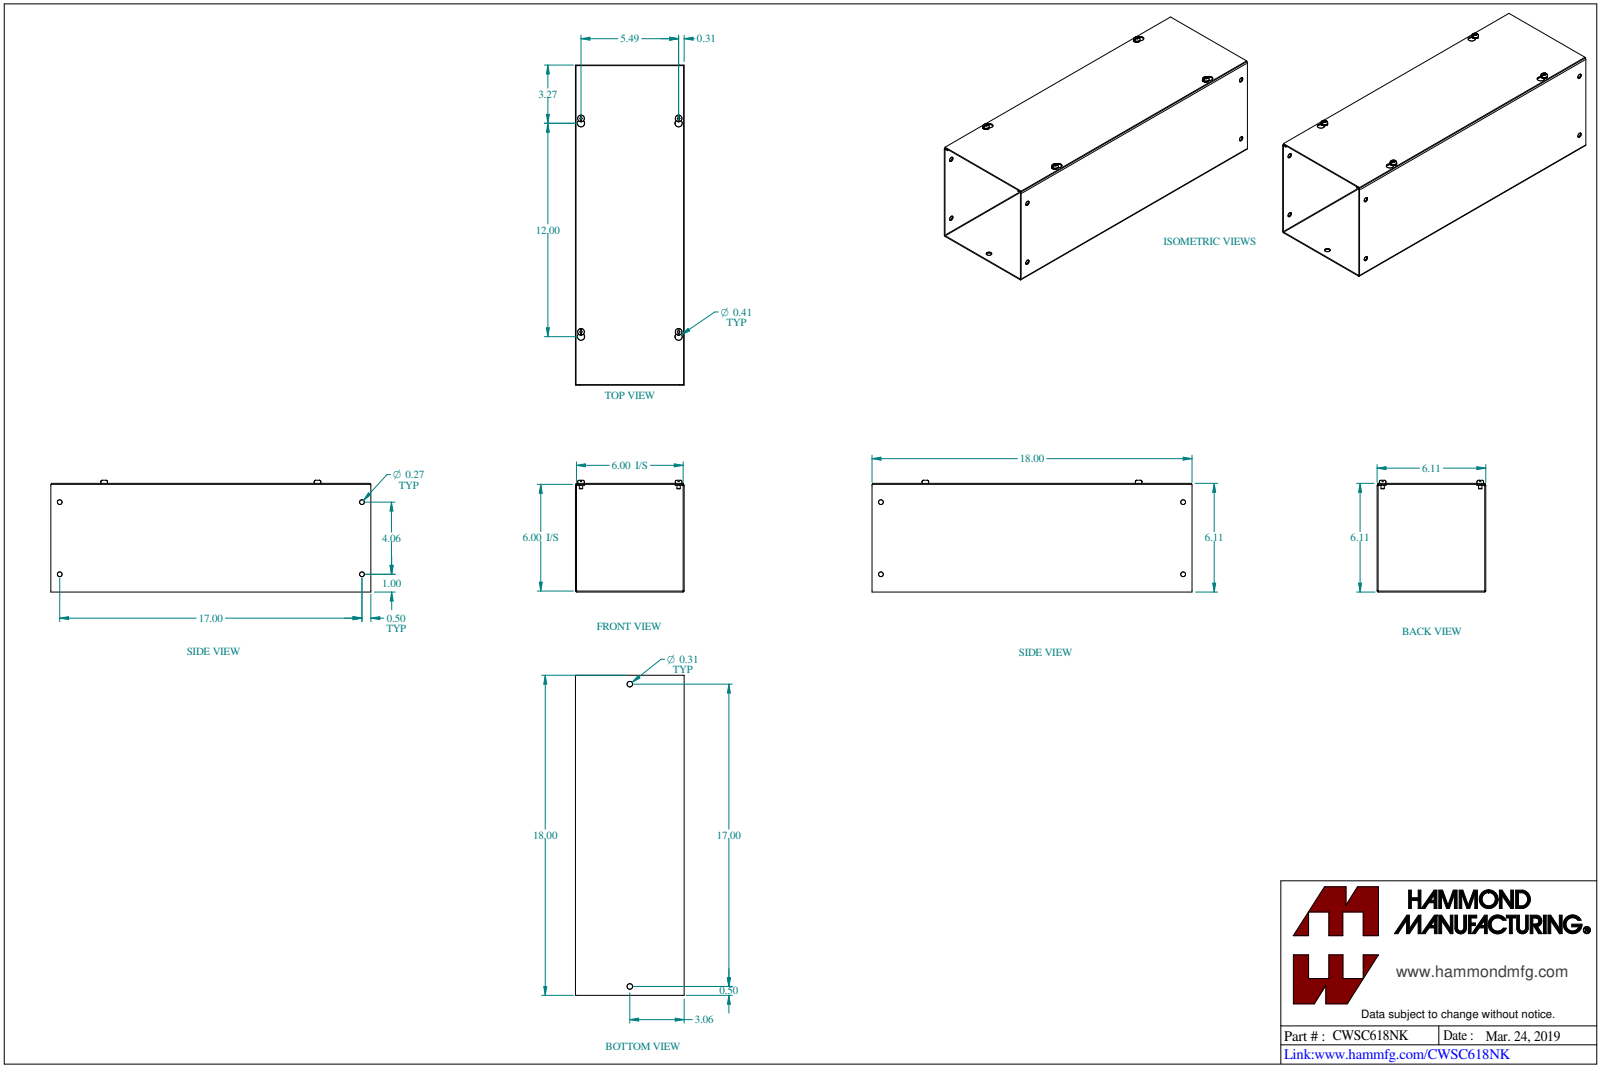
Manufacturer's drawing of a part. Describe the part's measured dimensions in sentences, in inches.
The part is named "CWSC618NK". Its 3-D file was written by "SolidWorks 2023 (CONFIG_CONTROL_DESIGN)". It is 6 solids with 180 faces: 88 planar, 68 cylindrical and 24 other. Overall it measures 18 by 6.289 by 6.114 inches. Its volume is 25.54 cubic inches and its surface area 903 square inches. Round holes: 4 of diameter 0.177, 4 of diameter 0.266, 2 of diameter 0.313. Round bosses or shafts: 4 of diameter 0.375, 4 of diameter 0.19. Partial cylindrical surfaces (rounded edges, fillets, slot ends): 4 of radius 0.029, 4 of radius 0.086, 4 of radius 0.125, 4 of radius 0.203. The main face-to-face distances are 0.057, 6.057, 6, 6.114, 5.943, 0.114, 0.031, 6.083, 0.026, 6.026. The hole center spacings are 3.713, 14.757, 17, 4.057, 5.489, 12, 13.196, 17.478.
